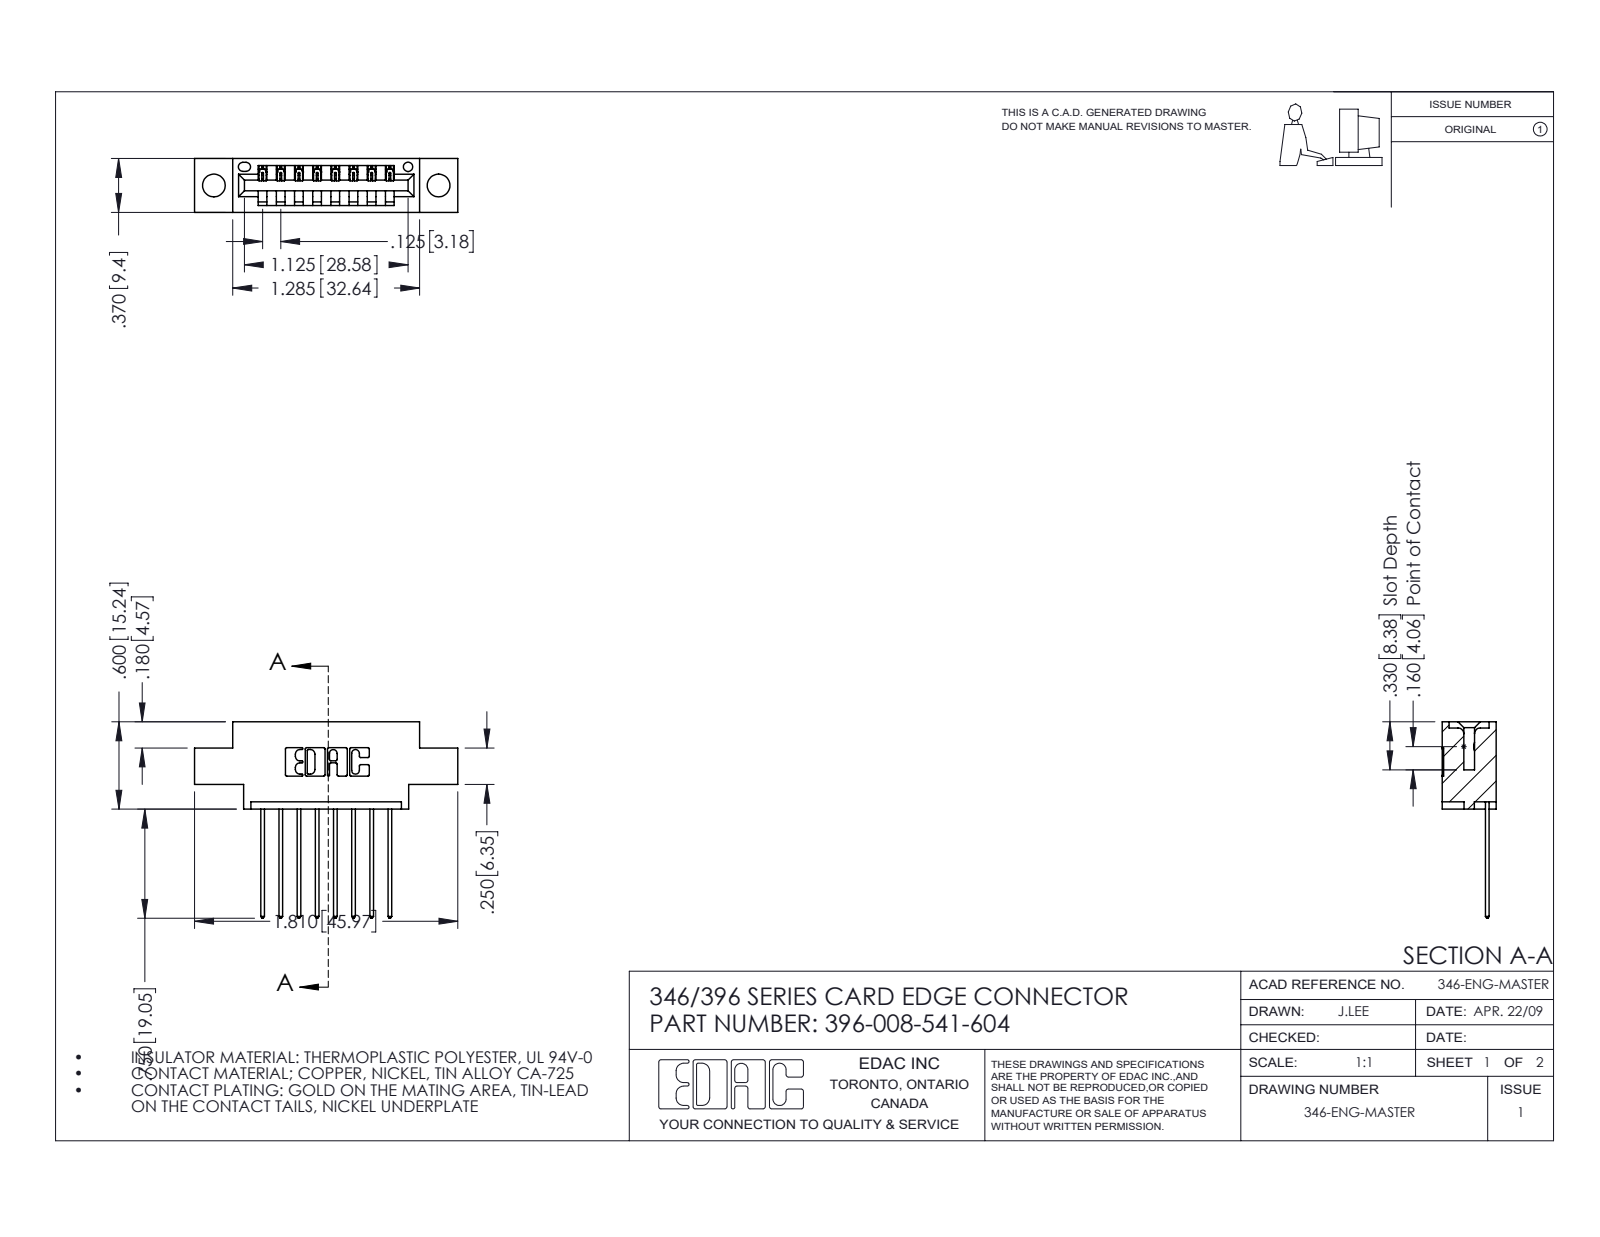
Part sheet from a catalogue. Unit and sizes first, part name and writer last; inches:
Units: inches
Overall size (bounding box): 1.81 × 1.35 × 0.37
Round holes (diameter × count): ⌀0.156 ×2, ⌀0.064 ×1
Partial cylindrical surfaces — rounded edges, fillets, slot ends (radius × count): R0.01 ×22, R0.006 ×16, R0.01 ×16, R0.007 ×6, R0.031 ×6, R0.026 ×3, R0.031 ×2, R0.04 ×2
Main face-to-face distances: 0.25, 0.37, 0.048, 0.322, 0.072, 0.298, 0.025, 0.148, 0.222, 0.1
Hole centre spacings: 0.246, 1.341, 1.545
Volume: 0.241 in³ · Surface area: 7.275 in²
Bodies: 9 solids, 590 faces (400 planar, 190 cylindrical, 0 other)
Part name (STEP PRODUCT): 346 Part_0.170 Offset - 0.156 Dia-TH; 345-292-001_345-293-141; 396-008-541-604
STEP written by: SolidWorks 2016 (CONFIG_CONTROL_DESIGN)
